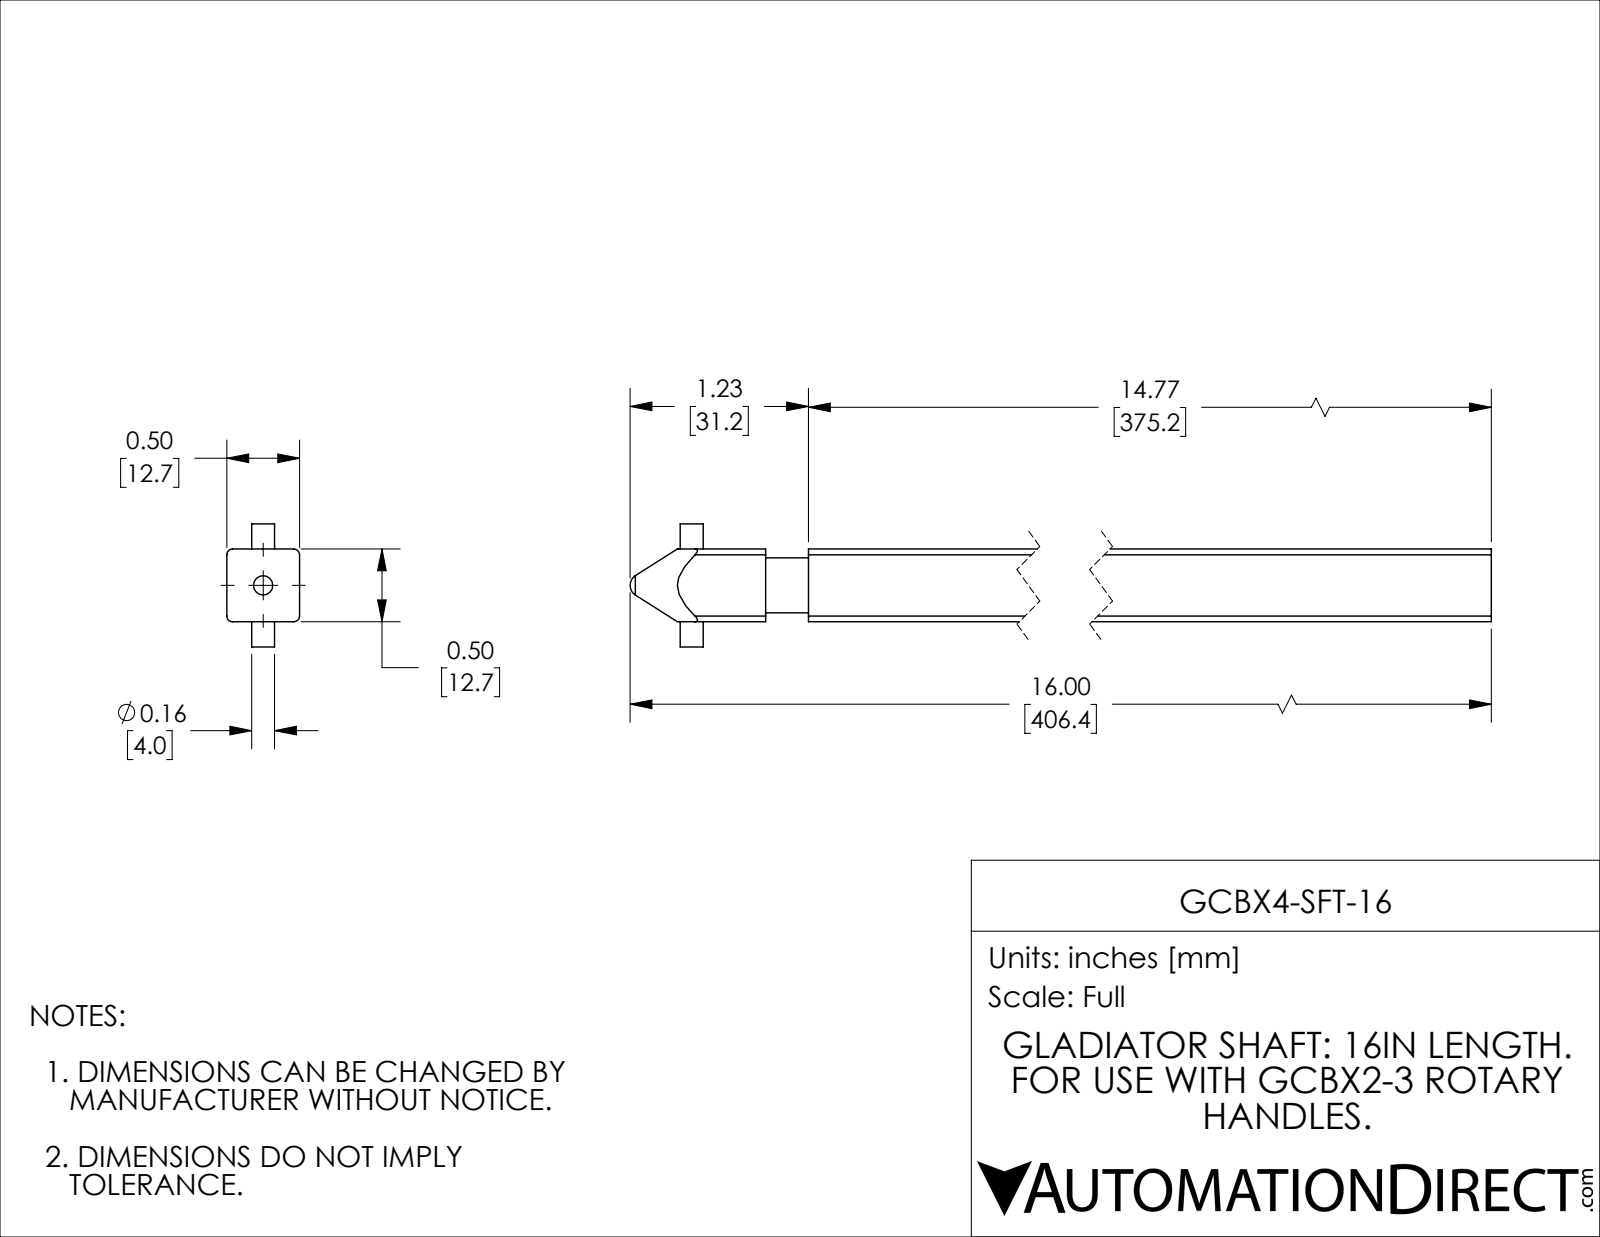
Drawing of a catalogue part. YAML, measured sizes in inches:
part_name: "GCBX4-SFT-16"
step_written_by: "SolidWorks 2021 (CONFIG_CONTROL_DESIGN)"
units: inches
bodies: {solids: 1, faces: 39, planar: 15, cylindrical: 17, other: 7}
overall_size: [15.999, 0.846, 0.5]
volume: 3.874
surface_area: 31.49
round_holes:
  - {diameter: 0.142, count: 1}
round_bosses_or_shafts:
  - {diameter: 0.378, count: 1}
  - {diameter: 0.157, count: 1}
partial_cylinders:
  - {radius: 0.039, count: 4}
face_to_face_distances: [0.5, 14.773, 15.068, 0.295, 0.244, 0.256, 0.173, 0.673, 0.846]
